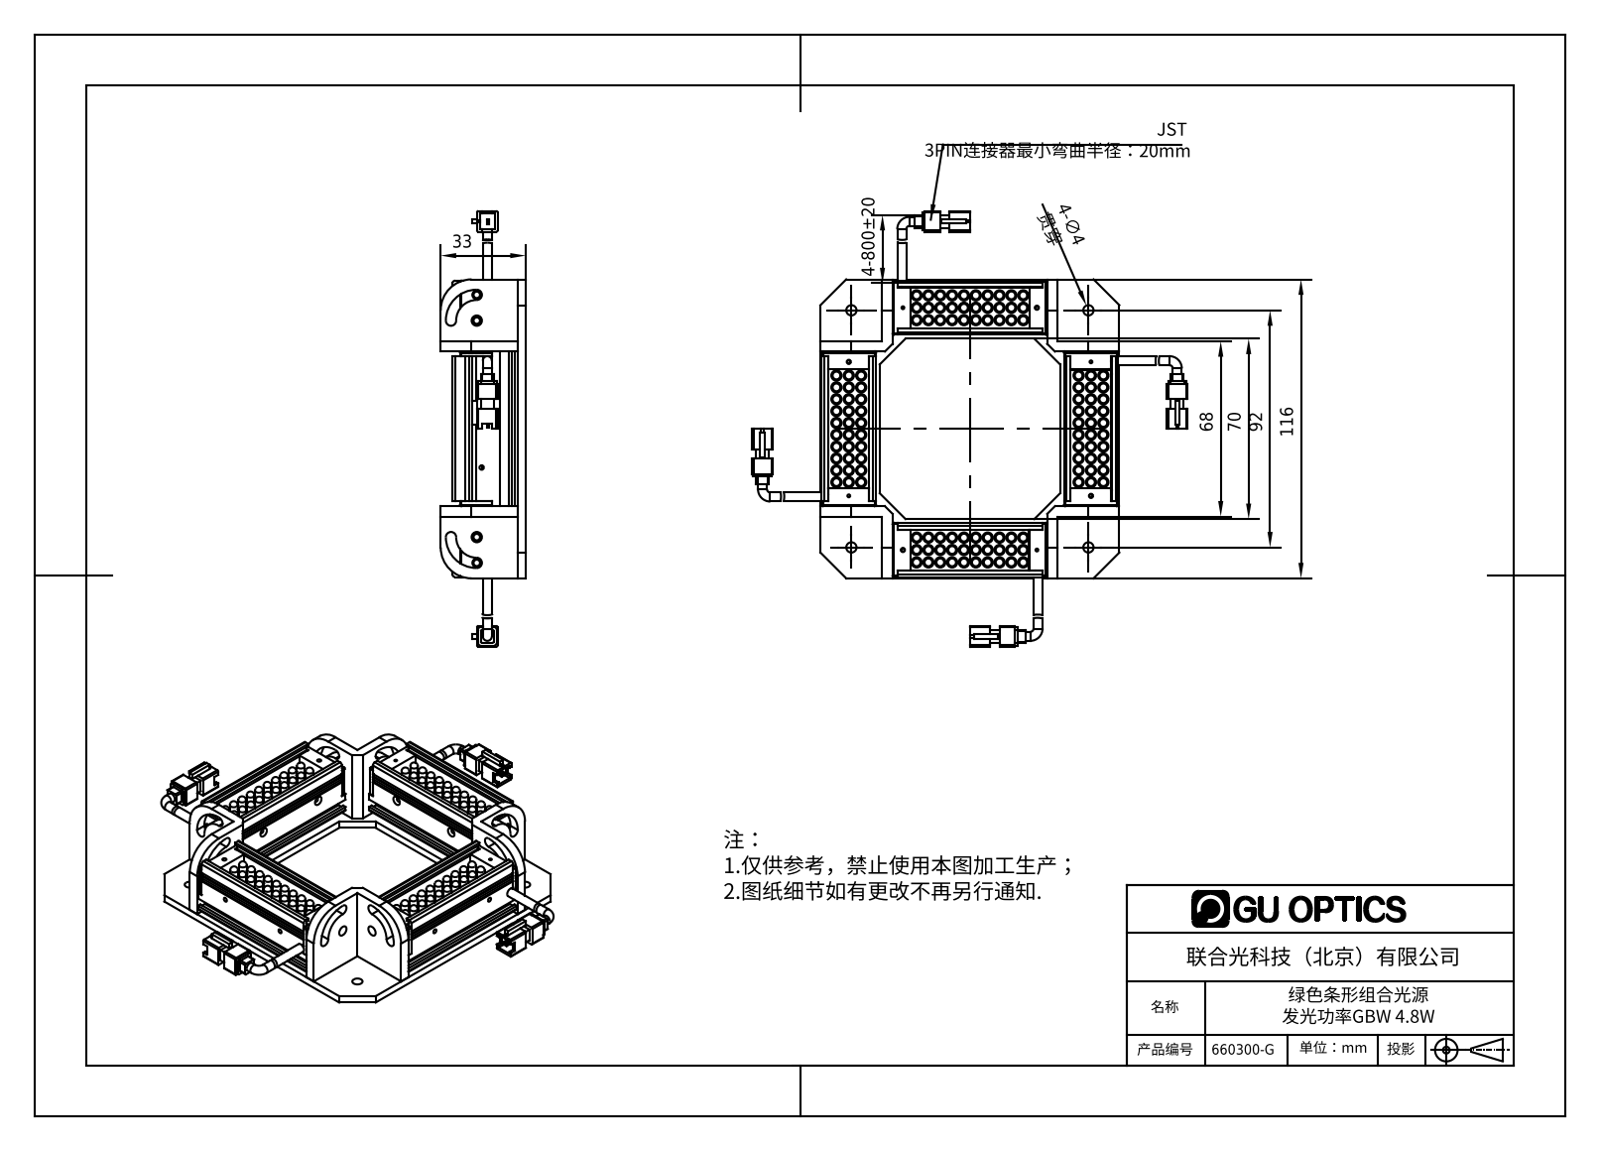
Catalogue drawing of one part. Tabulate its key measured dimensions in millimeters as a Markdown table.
| quantity | value |
| --- | --- |
| part name | 660300-G |
| STEP written by | SolidWorks 2016 (AUTOMOTIVE_DESIGN) |
| units | millimeters |
| bodies | 33 solids, 2177 faces (984 planar, 848 cylindrical, 345 other) |
| overall size | 169 × 169 × 33 |
| volume | 124 949 mm³ |
| surface area | 109 545 mm² |
| round holes (diameter × count) | 1.6 × 12, 2.5 × 8, 3 × 8, 4 × 8, 1.1 × 4, 1.25 × 4, 1.7 × 4, 2 × 4 |
| round bosses / shafts (diameter × count) | 4 × 120, 3 × 120, 3.5 × 8 |
| partial cylindrical surfaces (radius × count) | 1 × 48, 0.5 × 32, 2 × 8, 12 × 8, 1.65 × 4, 8 × 4 |
| main face-to-face distances | 2.5, 4, 3, 18.5, 9.9, 12.9, 91.5, 21, 94, 16.9 |
| hole center spacings | 16.38, 20.02, 26.23, 52, 68.09, 72.01, 75.96, 78.08 |
